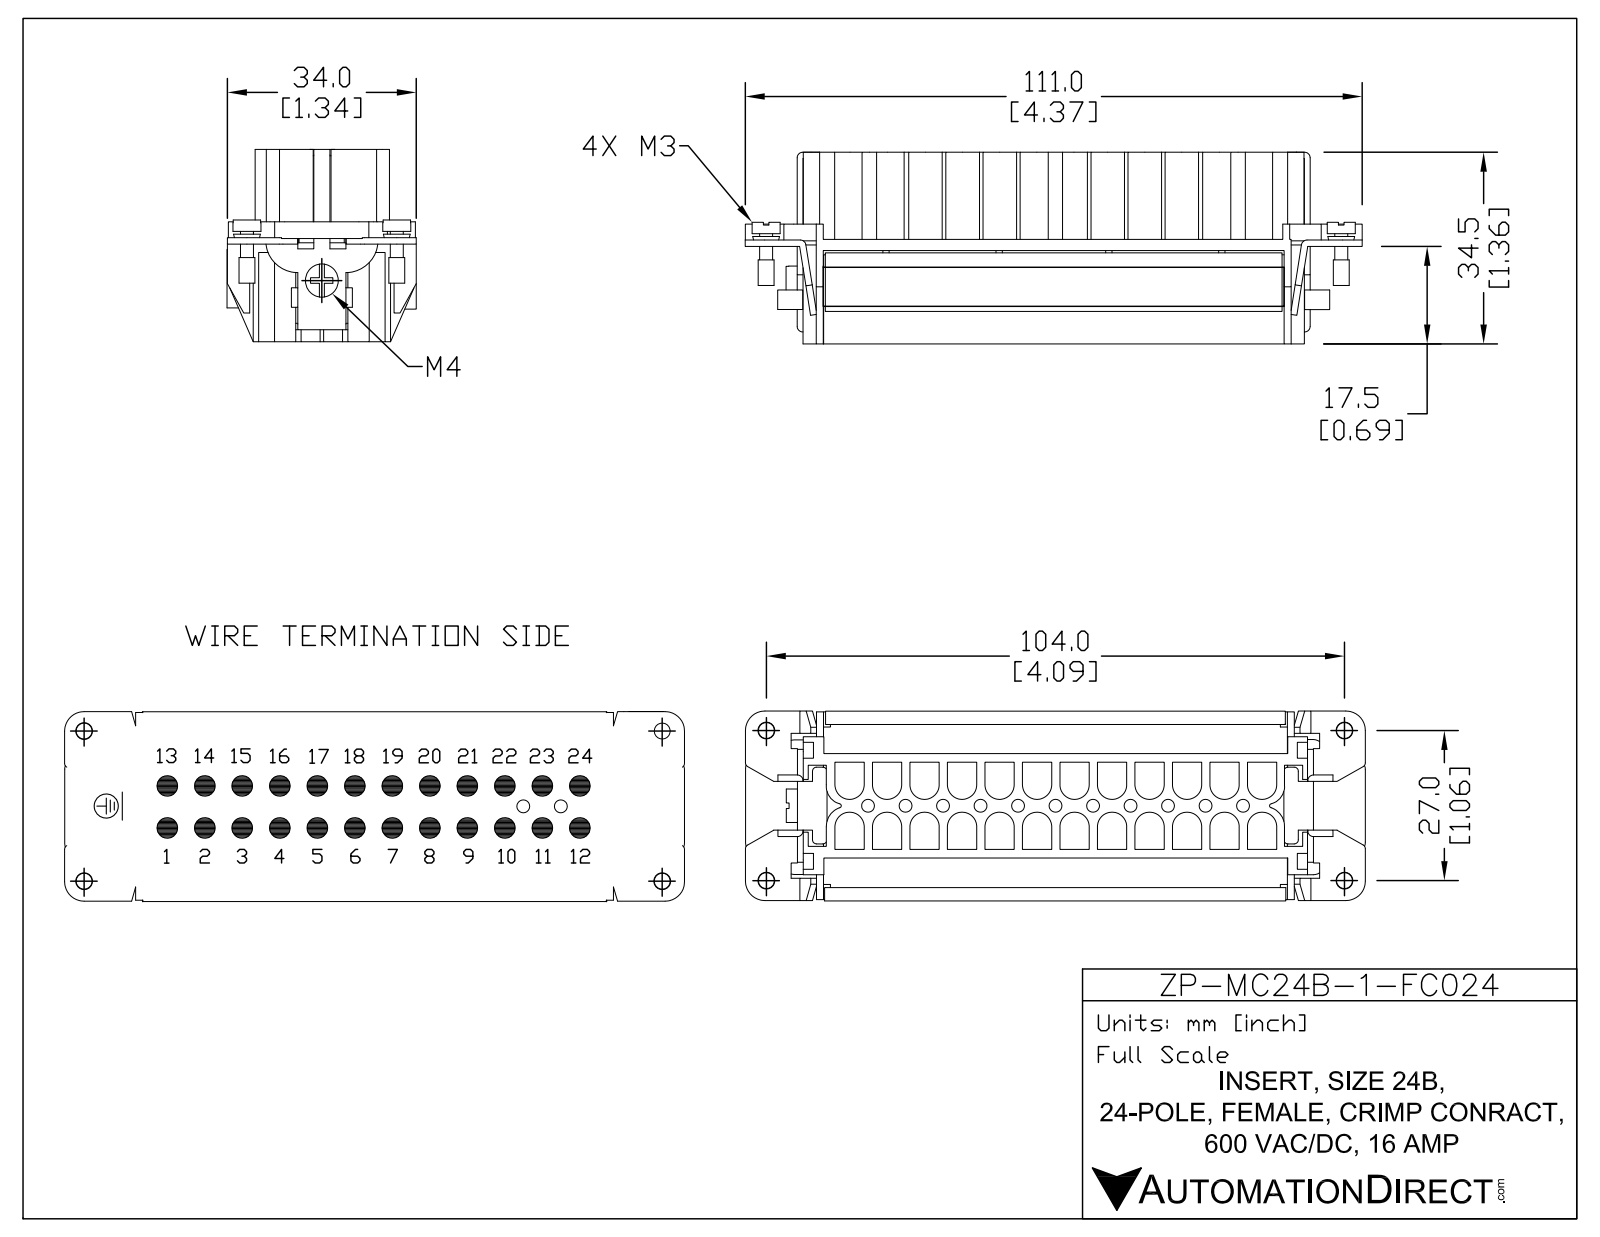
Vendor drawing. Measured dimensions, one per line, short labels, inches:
name: ZP-24B-24-FC-INSERT
written by: SolidWorks 2011 (AUTOMOTIVE_DESIGN)
unit: in
bodies: 1 solid, 1253 faces (935 planar, 252 cylindrical, 66 other)
size: 4.38 × 1.358 × 1.341
volume: 3.073 in³; area: 65.06 in²
holes: 20× ⌀0.225, 12× ⌀0.187, 11× ⌀0.069, 11× ⌀0.091, 4× ⌀0.119, 1× ⌀0.118
bosses: 4× ⌀0.198, 4× ⌀0.112, 4× ⌀0.091, 3× ⌀0.1, 1× ⌀0.236
rounds: 24× R0.103, 24× R0.103, 12× R0.03, 12× R0.039, 4× R0.07, 4× R0.079, 4× R0.085, 4× R0.113
face distances: 0.108, 0.364, 0.472, 0.276, 0.197, 0.089, 0.061, 0.03, 0.118, 0.094
hole spacings: 0.262, 0.266, 0.393, 0.265, 0.531, 1.063, 0.524, 0.53
